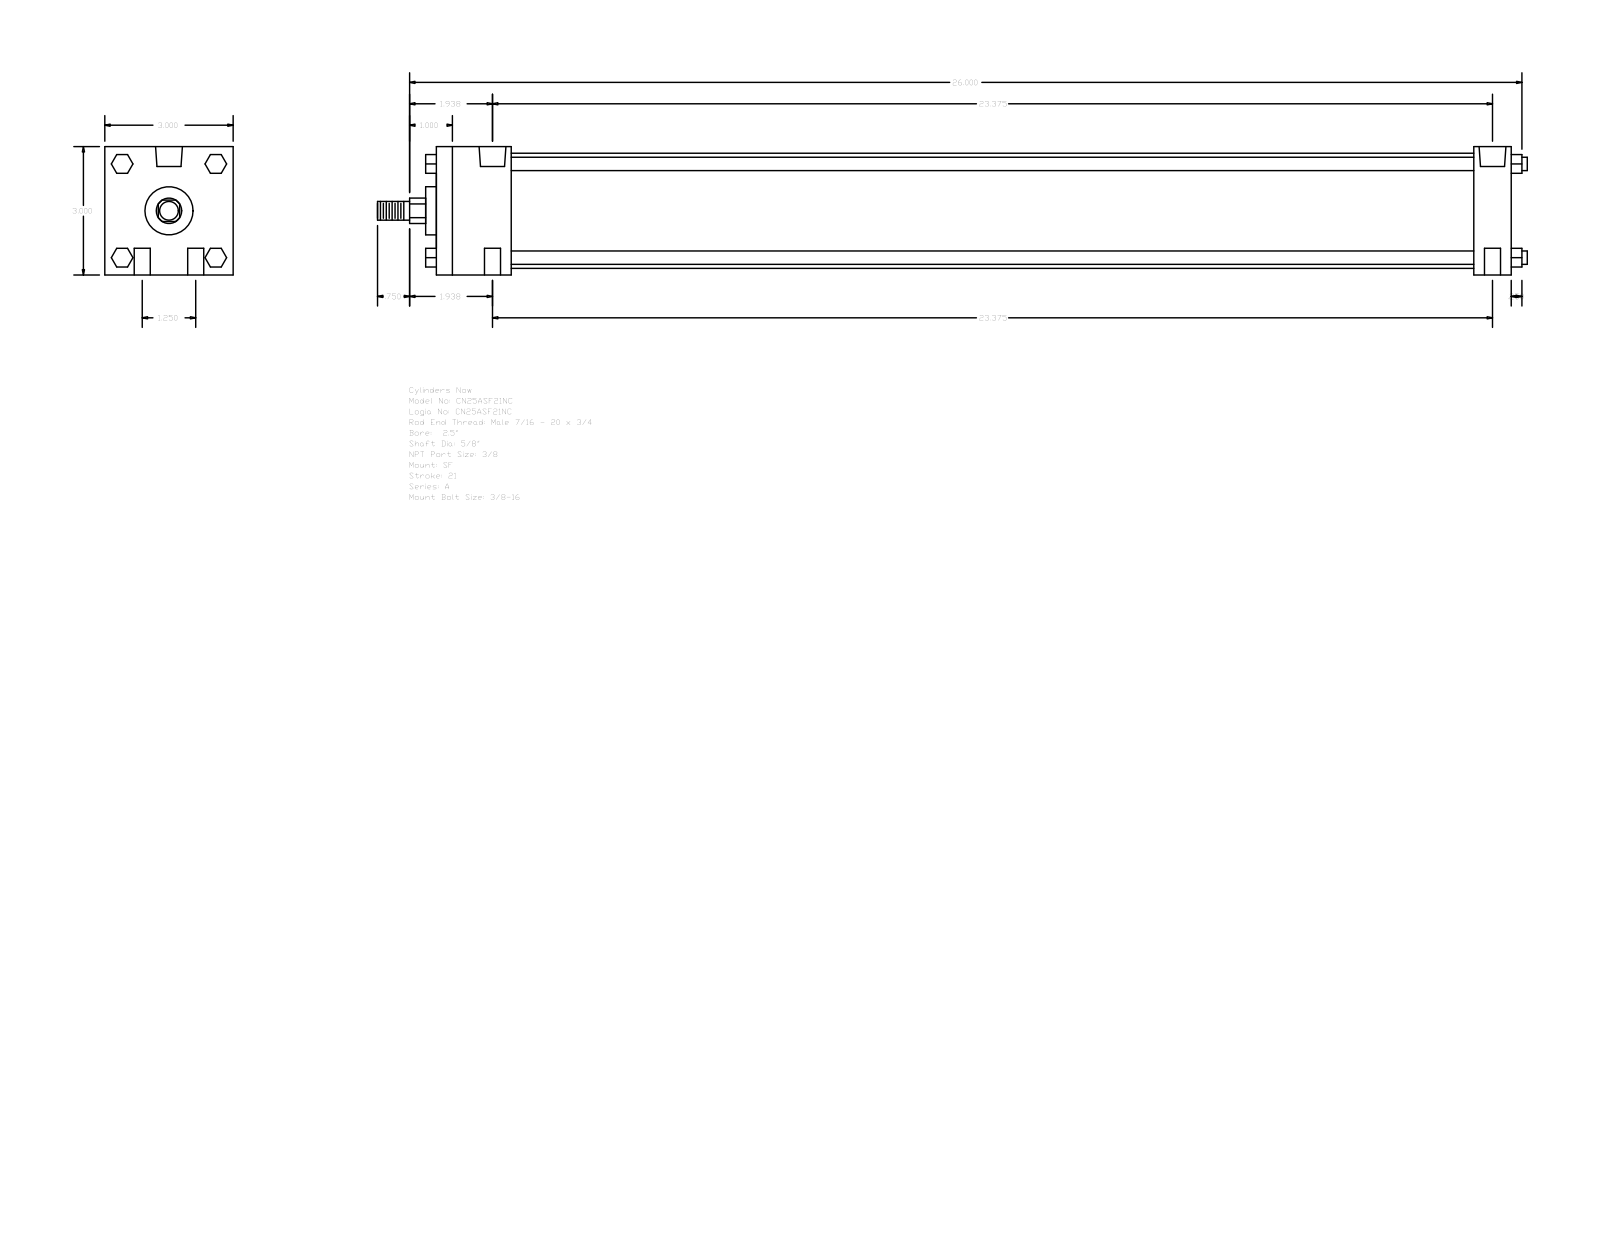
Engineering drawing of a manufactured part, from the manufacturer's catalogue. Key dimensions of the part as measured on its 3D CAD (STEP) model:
Part name (STEP PRODUCT): A_SF__0250_0.625
STEP written by: GSSL Pune (CONFIG_CONTROL_DESIGN)
Units: millimetres
Bodies: 0 solids, 124 faces (94 planar, 30 cylindrical, 0 other)
Overall size (bounding box): 682.62 × 76.2 × 76.2
Round holes (diameter × count): ⌀9.53 ×4, ⌀5.56 ×2, ⌀15.93 ×2
Round bosses / shafts (diameter × count): ⌀7.94 ×4, ⌀68.33 ×1, ⌀28.57 ×1, ⌀15.88 ×1, ⌀11.11 ×1
Partial cylindrical surfaces — rounded edges, fillets, slot ends (radius × count): R7.54 ×1
Main face-to-face distances: 76.2, 638.17, 44.45, 615.95, 22.22, 571.5, 593.72, 6.35, 644.52, 50.8
Hole centre spacings: 15.88, 593.94, 593.73, 31.76, 594.58, 598.49
